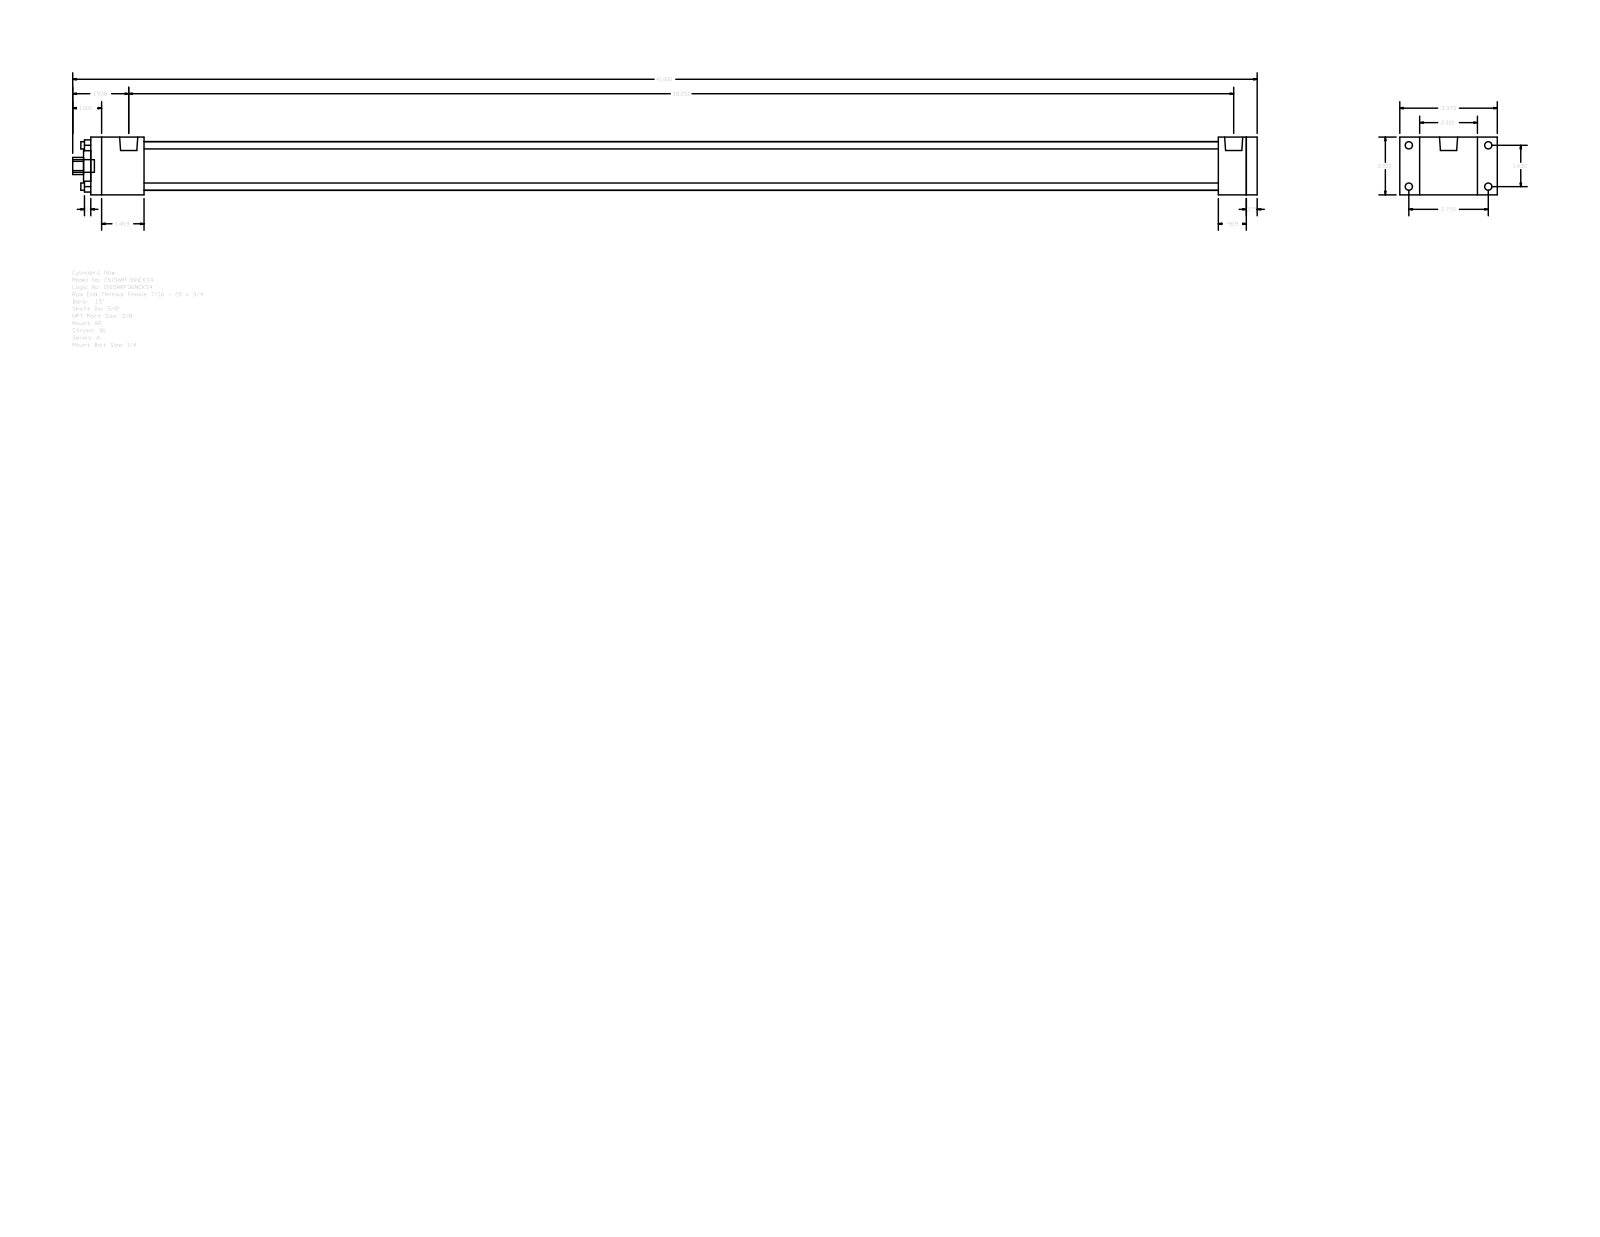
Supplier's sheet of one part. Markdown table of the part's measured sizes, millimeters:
| quantity | value |
| --- | --- |
| part name | A_RF__0150_0.625 |
| STEP written by | GSSL Pune (CONFIG_CONTROL_DESIGN) |
| units | millimeters |
| bodies | 0 solids, 92 faces (64 planar, 28 cylindrical, 0 other) |
| overall size | 1041.4 × 85.72 × 50.8 |
| round holes (diameter × count) | 6.35 × 4, 15.88 × 1, 28.57 × 1, 42.93 × 1 |
| round bosses / shafts (diameter × count) | 6.35 × 4, 5.56 × 4, 15.93 × 2, 11.11 × 1 |
| partial cylindrical surfaces (radius × count) | 7.54 × 1 |
| main face-to-face distances | 50.8, 9.52, 1016, 1025.52, 991.39, 24.61, 34.13, 46.83, 944.56, 969.17 |
| hole center spacings | 25.68, 36.32, 51.36 |
